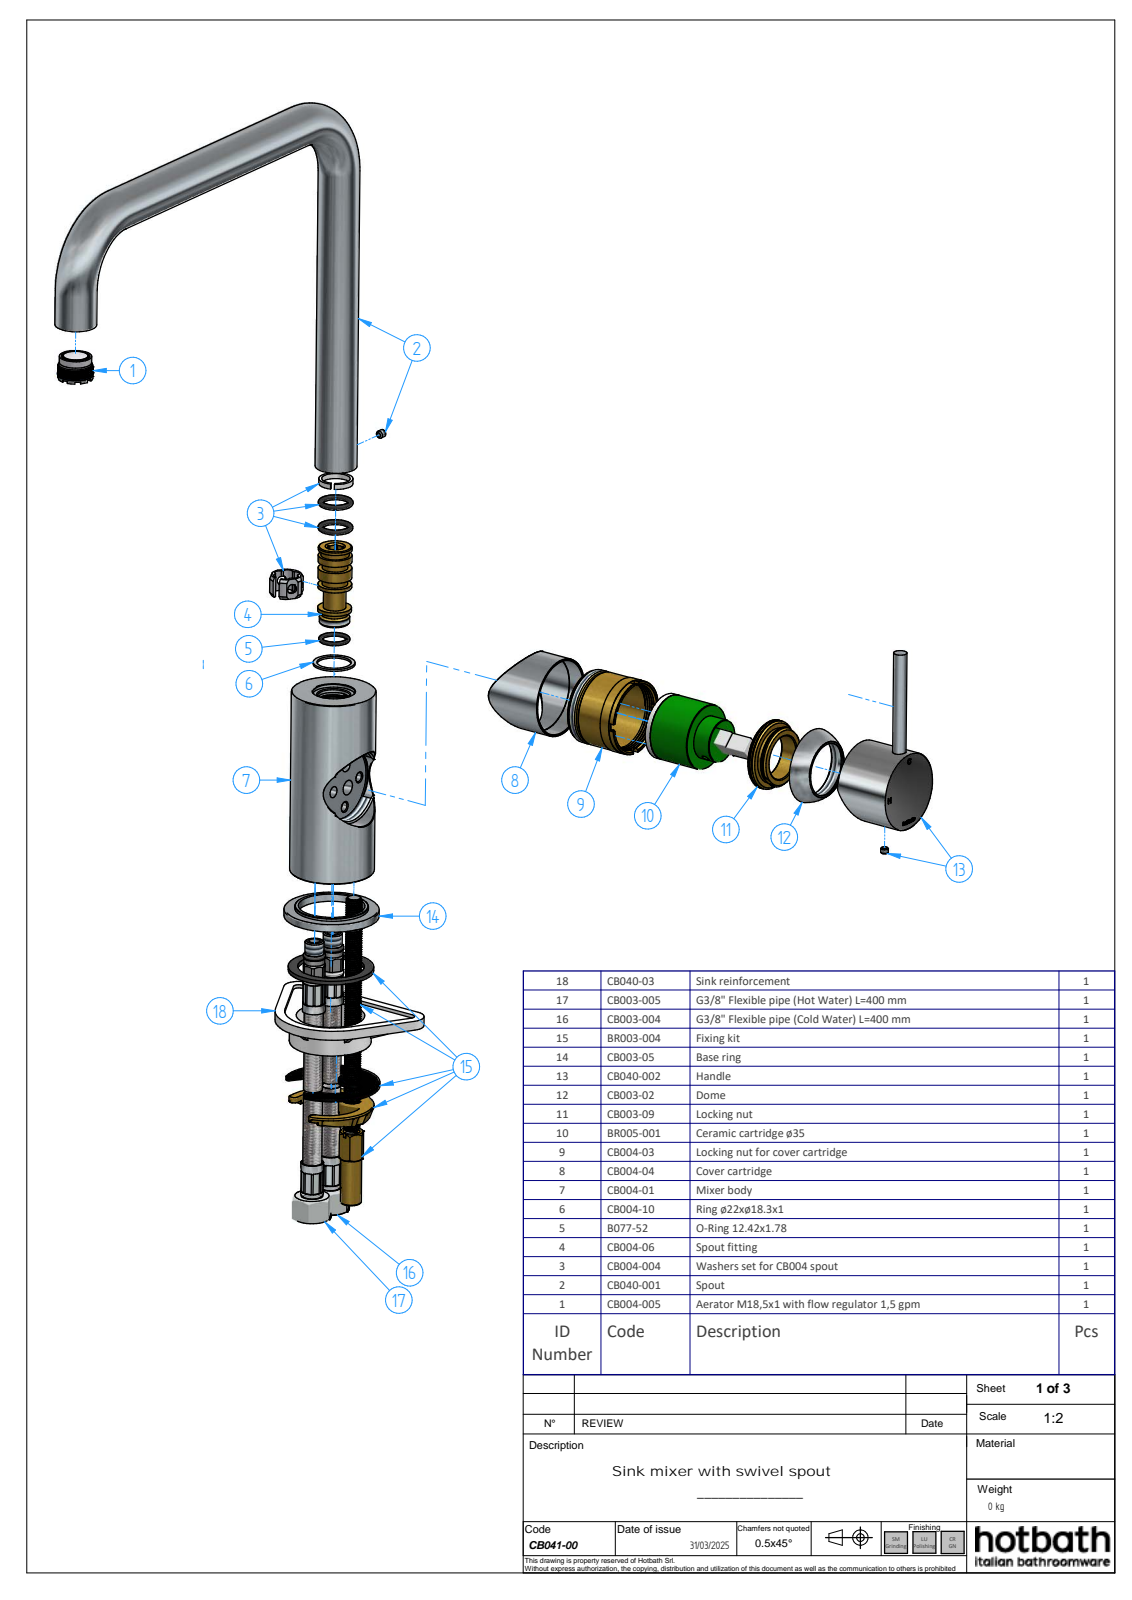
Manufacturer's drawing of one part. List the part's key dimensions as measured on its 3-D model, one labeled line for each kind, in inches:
Part name (STEP PRODUCT): CB041-00; CB040-002_oa_0; CB004-05; CB040-02 (+8 more)
STEP written by: Solid Edge (AUTOMOTIVE_DESIGN)
Units: inches
Bodies: 9 solids, 1093 faces (653 planar, 308 cylindrical, 132 other)
Overall size (bounding box): 12.39 × 10.472 × 3.876
Volume: 11.07 in³ · Surface area: 173.1 in²
Round holes (diameter × count): ⌀0.03 ×116, ⌀0.197 ×4, ⌀0.236 ×4, ⌀0.315 ×3, ⌀0.433 ×3, ⌀0.709 ×3, ⌀0.354 ×2, ⌀1.535 ×2, ⌀0.13 ×1, ⌀0.165 ×1, ⌀0.262 ×1, ⌀0.268 ×1
Round bosses / shafts (diameter × count): ⌀0.866 ×3, ⌀1.969 ×1, ⌀1.654 ×1, ⌀1.524 ×1, ⌀0.728 ×1, ⌀0.724 ×1, ⌀0.686 ×1, ⌀0.685 ×1
Partial cylindrical surfaces — rounded edges, fillets, slot ends (radius × count): R0.004 ×4, R0.433 ×4, R0.197 ×2, R0.019 ×1, R0.256 ×1, R0.354 ×1, R0.748 ×1, R0.783 ×1
Main face-to-face distances: 3.031, 3.937, 2.508, 0.906, 1.063, 0.098, 1.004, 4.035, 0.157, 0.059
Hole centre spacings: 0.121, 0.035, 0.04, 0.046, 0.047, 0.082, 0.086, 0.092
